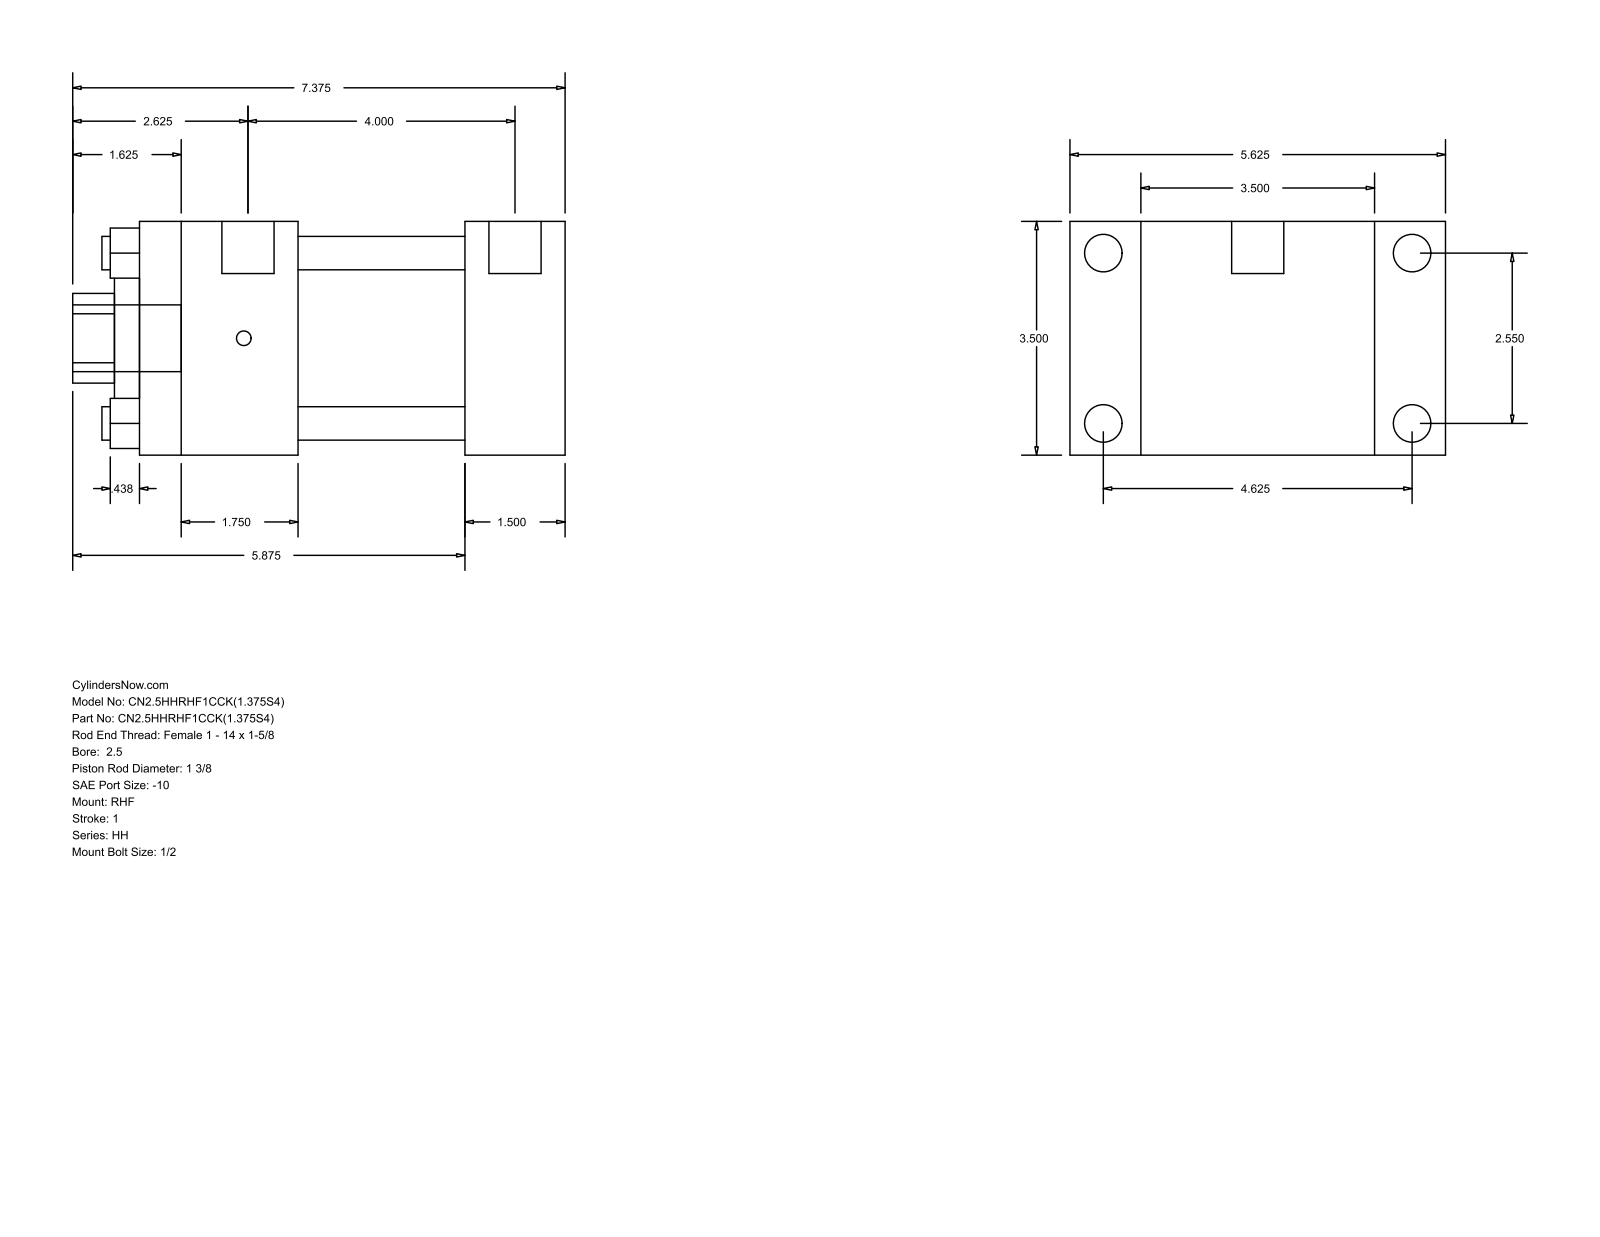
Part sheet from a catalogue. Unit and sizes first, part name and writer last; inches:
Units: inches
Overall size (bounding box): 7.375 × 5.625 × 3.5
Round holes (diameter × count): ⌀0.5 ×4, ⌀1.375 ×1, ⌀2 ×1, ⌀2.875 ×1
Round bosses / shafts (diameter × count): ⌀0.563 ×4, ⌀0.219 ×4, ⌀0.781 ×2, ⌀1 ×1
Partial cylindrical surfaces — rounded edges, fillets, slot ends (radius × count): R0.672 ×1
Main face-to-face distances: 3.5, 1.5, 1.063, 4.563, 4.875, 6.375, 5.625, 2.375, 2.5, 4
Hole centre spacings: 1.803, 2.55, 3.606
Bodies: 0 solids, 88 faces (60 planar, 28 cylindrical, 0 other)
Part name (STEP PRODUCT): HH_RHF__0250_1.375
STEP written by: GSSL Pune (CONFIG_CONTROL_DESIGN)
